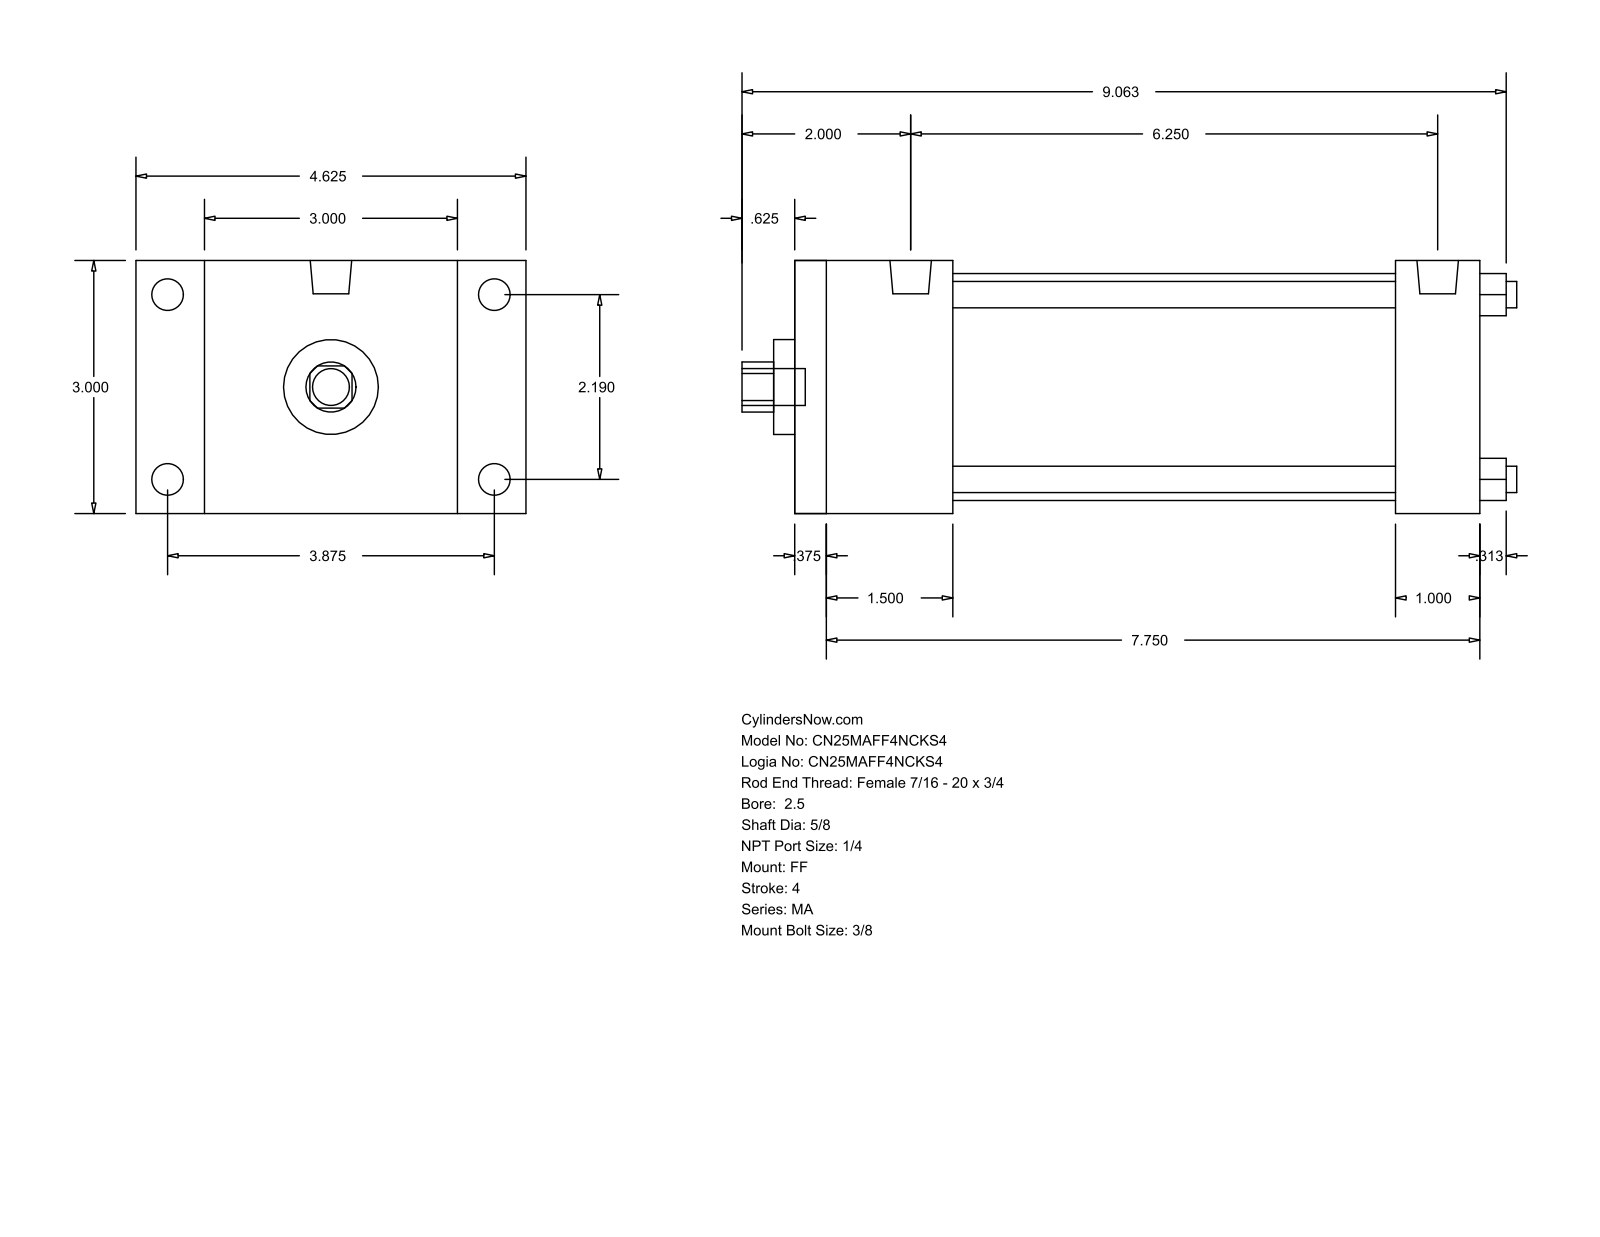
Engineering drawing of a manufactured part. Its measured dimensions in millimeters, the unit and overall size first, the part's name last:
Units: millimetres
Overall size (bounding box): 233.36 × 117.47 × 76.2
Round holes (diameter × count): ⌀7.94 ×4, ⌀15.88 ×1, ⌀28.57 ×1, ⌀68.33 ×1
Round bosses / shafts (diameter × count): ⌀9.53 ×4, ⌀7.94 ×4, ⌀12.49 ×2, ⌀11.11 ×1
Partial cylindrical surfaces — rounded edges, fillets, slot ends (radius × count): R7.54 ×1
Main face-to-face distances: 76.2, 206.37, 9.52, 196.85, 25.4, 47.62, 180.97, 38.1, 171.45, 133.35
Hole centre spacings: 39.33, 55.62, 78.66
Bodies: 0 solids, 92 faces (64 planar, 28 cylindrical, 0 other)
Part name (STEP PRODUCT): MA_FF__0250_0.625
STEP written by: GSSL Pune (CONFIG_CONTROL_DESIGN)
